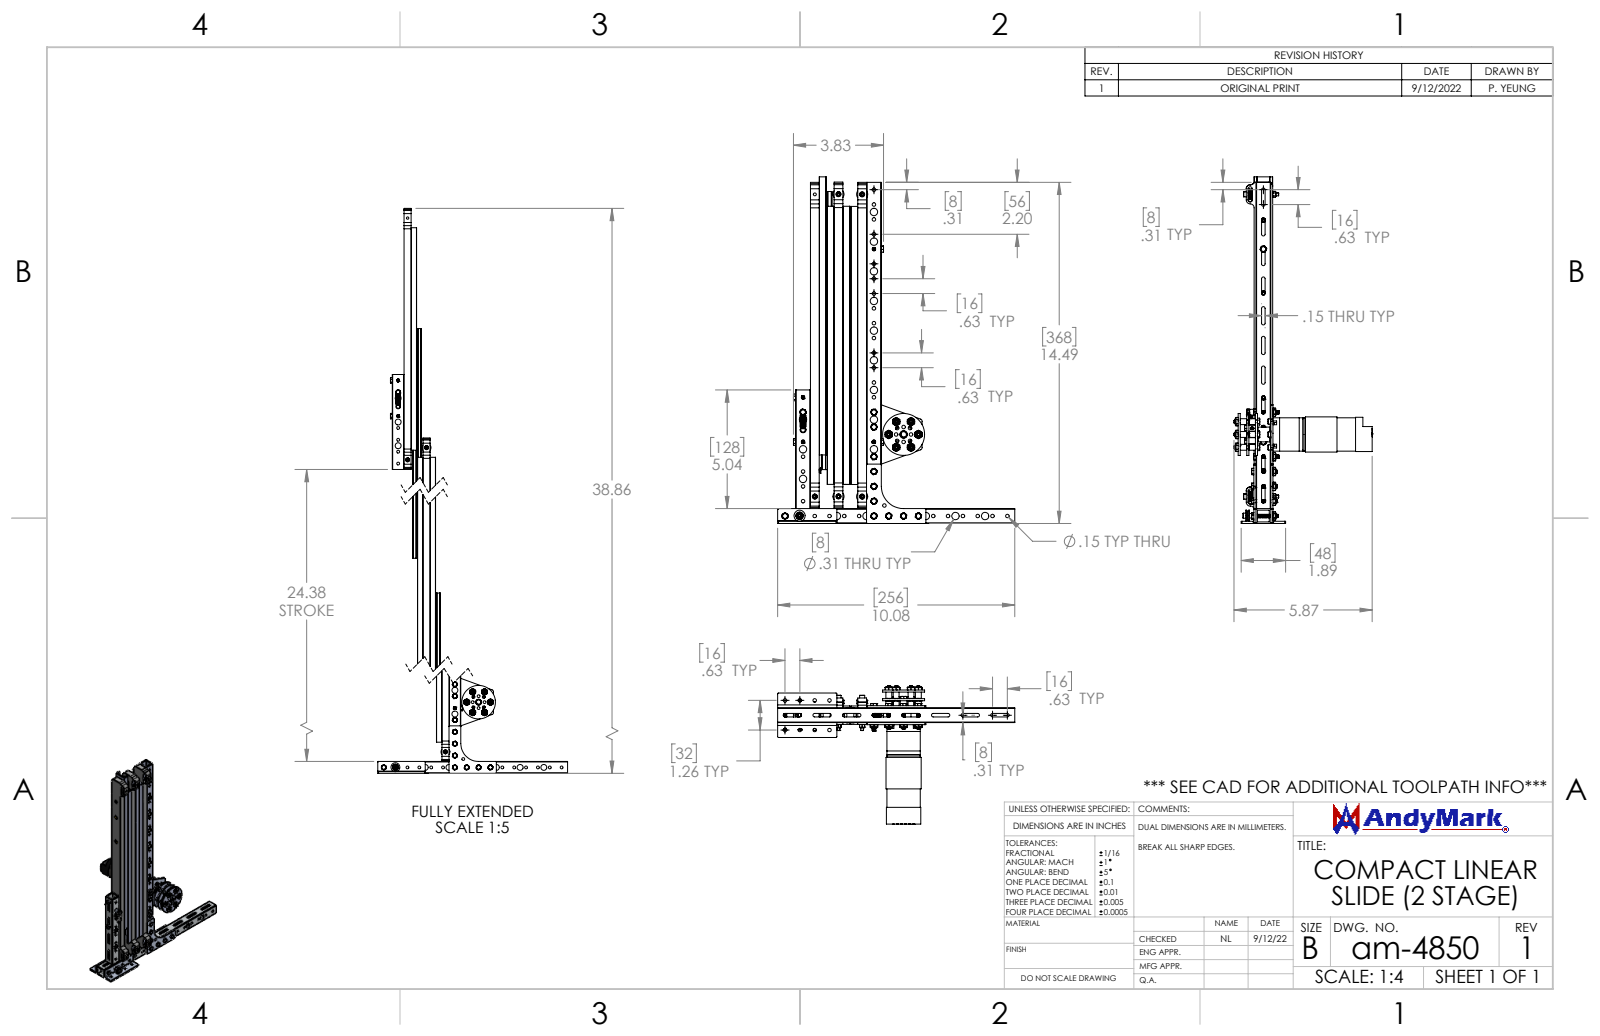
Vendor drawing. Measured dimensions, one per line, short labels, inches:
name: 625x500 Aluminum Spacer am-3720_92510A777; am-4376 17T 0.5mod NeveRest Orbital Pinion; M3-0.5 x 5mm SHCS_90128A187; 16mm Super Box Tubing concept 352mm (+8 more)
written by: SolidWorks 2022 (AUTOMOTIVE_DESIGN)
unit: in
bodies: 267 solids, 12760 faces (1490 planar, 5521 cylindrical, 5749 other)
size: 14.497 × 10.079 × 5.881
volume: 33.69 in³; area: 566.4 in²
holes: 69× ⌀0.15, 54× ⌀0.116, 26× ⌀0.315, 18× ⌀0.111, 18× ⌀0.191, 12× ⌀0.136, 12× ⌀0.15, 12× ⌀0.187, 11× ⌀0.118, 10× ⌀0.098, 10× ⌀0.125, 9× ⌀0.138
bosses: 25× ⌀0.138, 14× ⌀0.217, 12× ⌀0.218, 12× ⌀0.185, 12× ⌀0.178, 10× ⌀0.093, 9× ⌀0.118, 7× ⌀0.25
rounds: 80× R0.008, 38× R0.075, 36× R0.167, 34× R0.064, 18× R0.058, 16× R0.075, 13× R0.039, 12× R0.01
face distances: 0.63, 1.005, 0.567, 0.063, 1.005, 2.01, 0.079, 0.709, 0.375, 1.38
hole spacings: 1.26, 0.63, 1.89, 2.52, 2.205, 4.094, 3.78, 0.315
